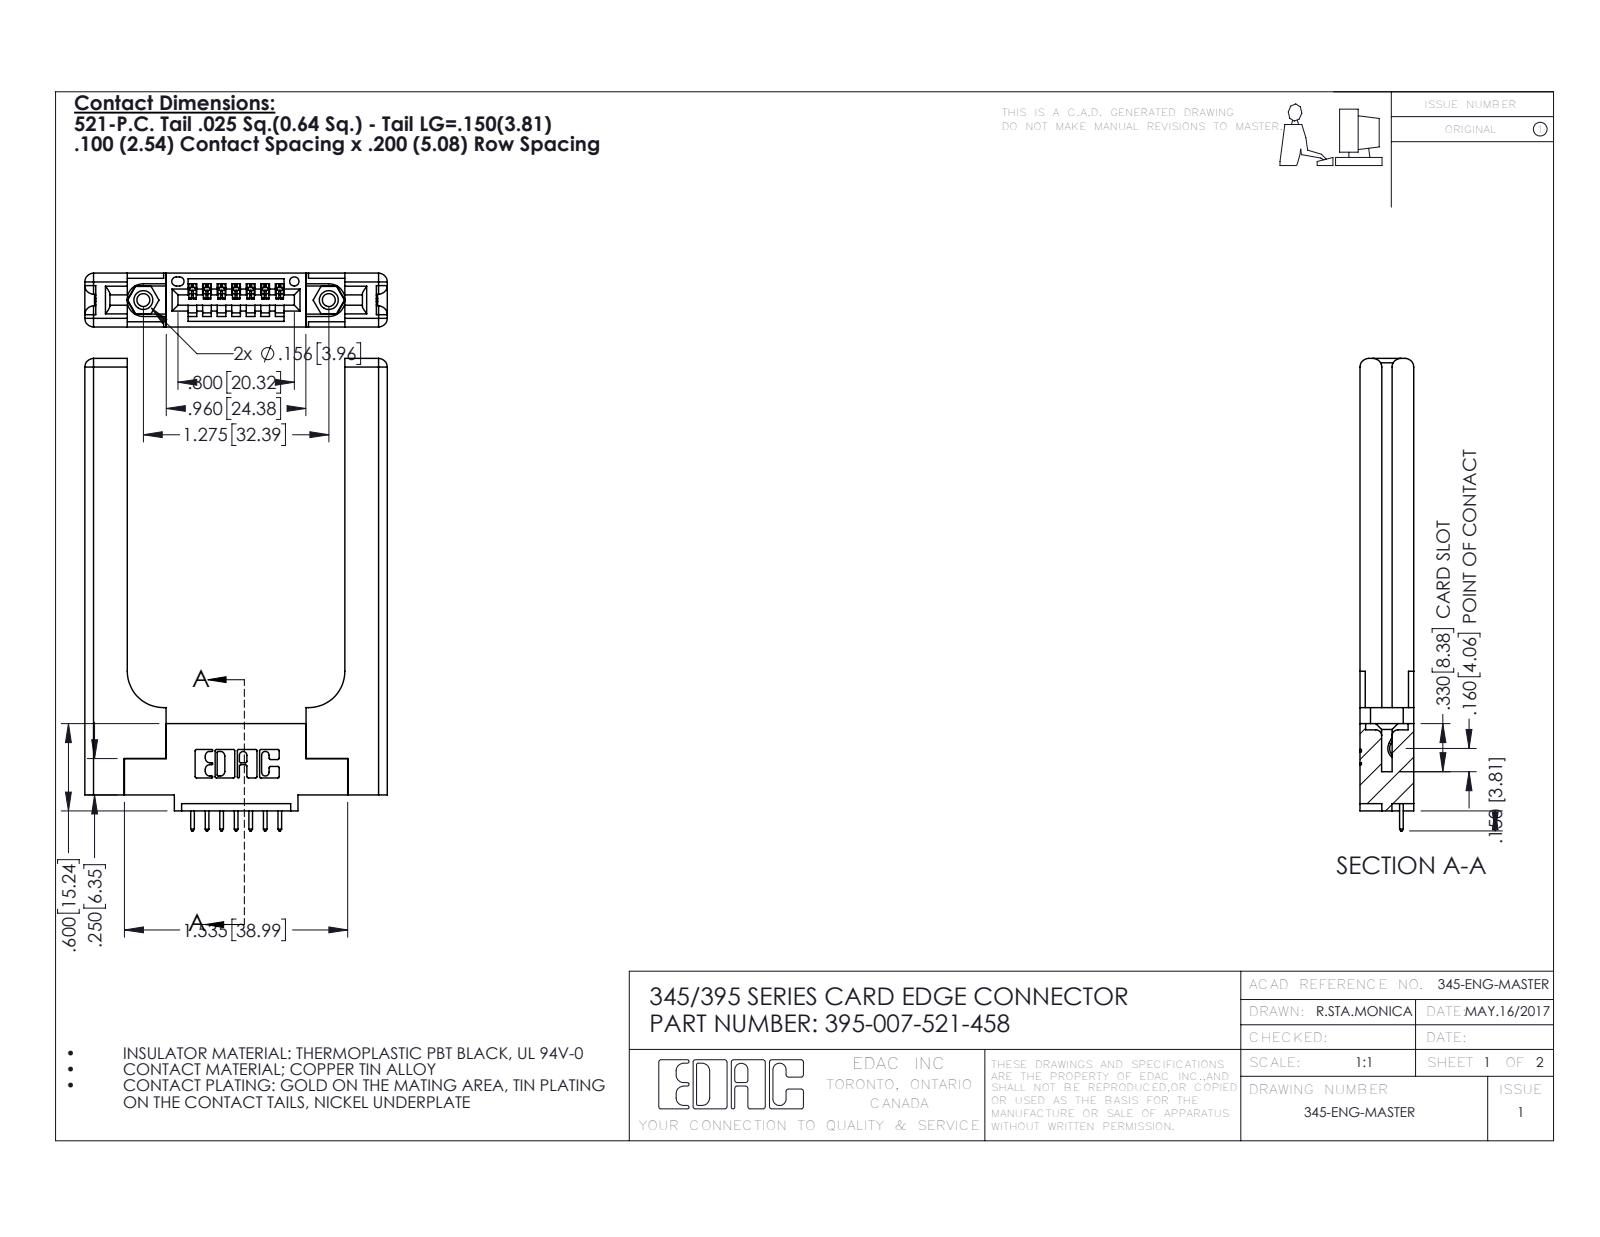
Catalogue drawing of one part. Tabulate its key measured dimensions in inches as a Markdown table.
| quantity | value |
| --- | --- |
| part name | 345-292-001_345-293-121; 345 Part_0.110 Offset - 0.156 Dia-TH; 345-220-058_345-220-058; 345-250-001_345-250-001-102 (+1 more) |
| STEP written by | SolidWorks 2016 (CONFIG_CONTROL_DESIGN) |
| units | inches |
| bodies | 12 solids, 792 faces (512 planar, 220 cylindrical, 60 other) |
| overall size | 3.247 × 2.079 × 0.37 |
| volume | 0.802 in³ |
| surface area | 17.04 in² |
| round holes (diameter × count) | 0.089 × 2, 0.125 × 2, 0.156 × 2, 0.064 × 1 |
| round bosses / shafts (diameter × count) | 0.155 × 2 |
| partial cylindrical surfaces (radius × count) | 0.01 × 22, 0.06 × 16, 0.006 × 14, 0.01 × 14, 0.007 × 6, 0.031 × 6, 0.026 × 3, 0.03 × 2 |
| main face-to-face distances | 0.37, 0.15, 0.22, 0.072, 0.148, 0.077, 1.496, 0.298, 0.071, 0.292 |
| hole center spacings | 0.27, 1.045, 1.275 |
